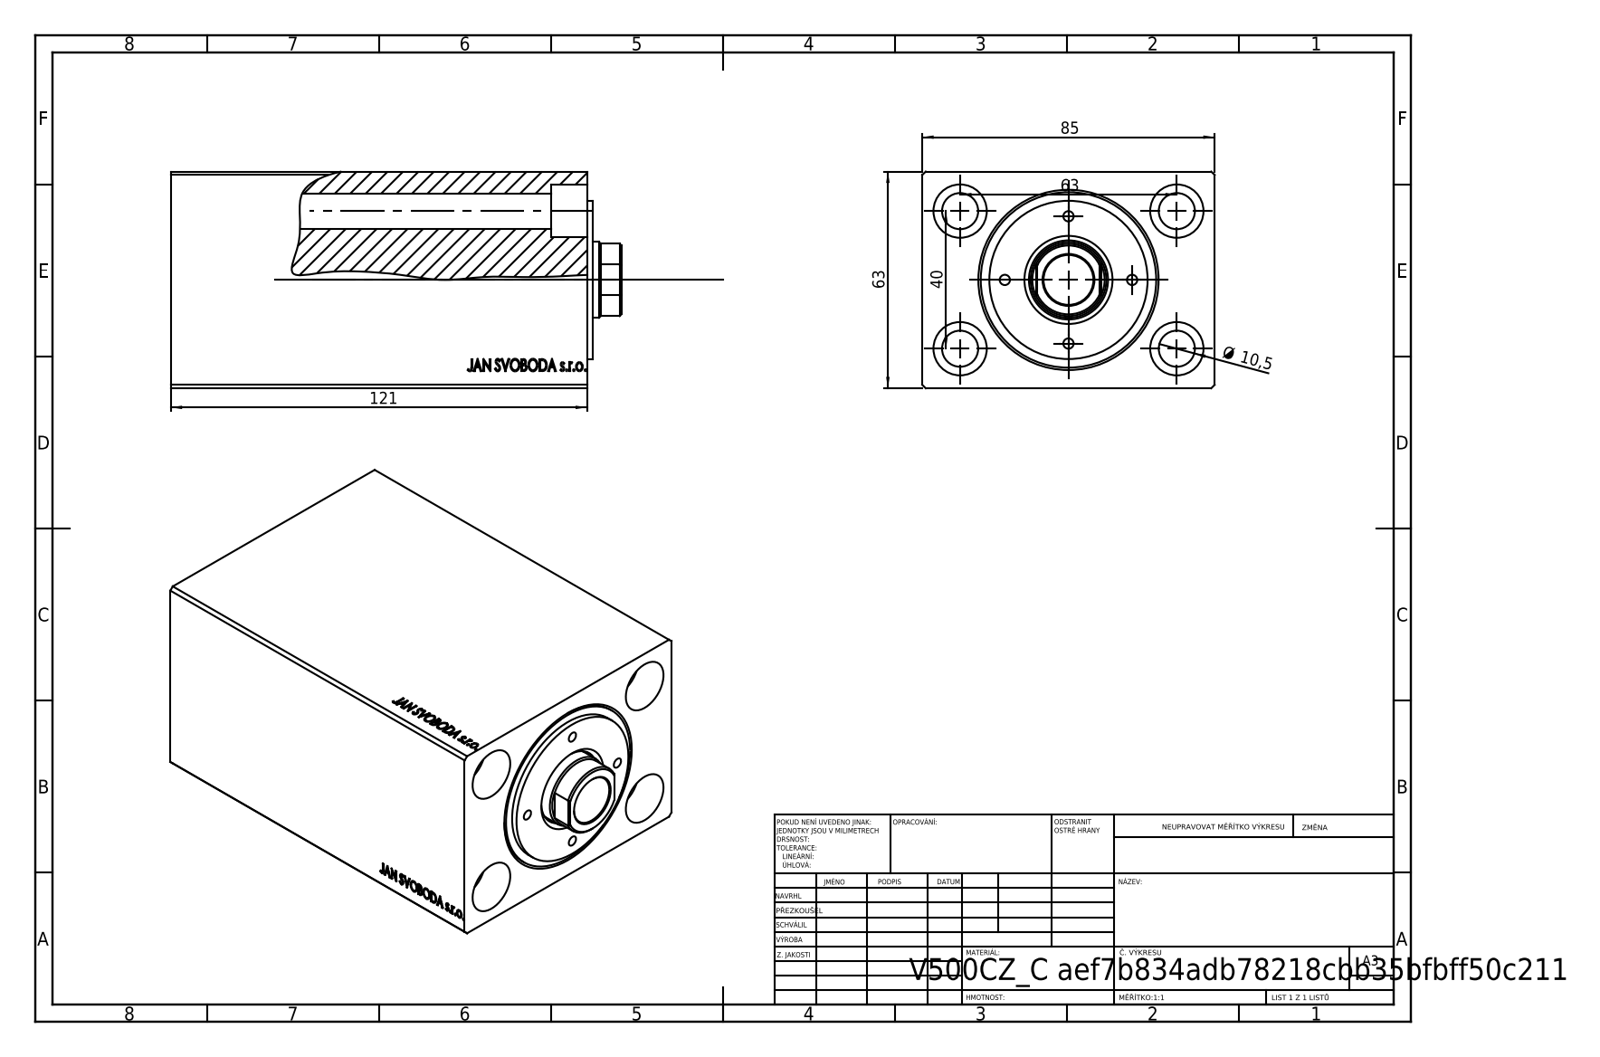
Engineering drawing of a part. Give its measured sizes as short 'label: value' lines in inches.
written by: SolidWorks 2019 (CONFIG_CONTROL_DESIGN)
unit: in
bodies: 1 solid, 818 faces (394 planar, 42 cylindrical, 382 other)
size: 4.764 × 3.346 × 2.48
volume: 24.62 in³; area: 124.1 in²
holes: 4× ⌀0.413, 4× ⌀0.61, 2× ⌀0.217, 2× ⌀0.535, 2× ⌀0.787, 1× ⌀1.417, 1× ⌀1.575, 1× ⌀2.008
face distances: 2.48, 3.346, 4.764, 4.185, 0.579, 4.756, 0.571, 0.407, 4.357, 2.795
hole spacings: 1.469, 1.575, 2.48, 2.938, 3.268
